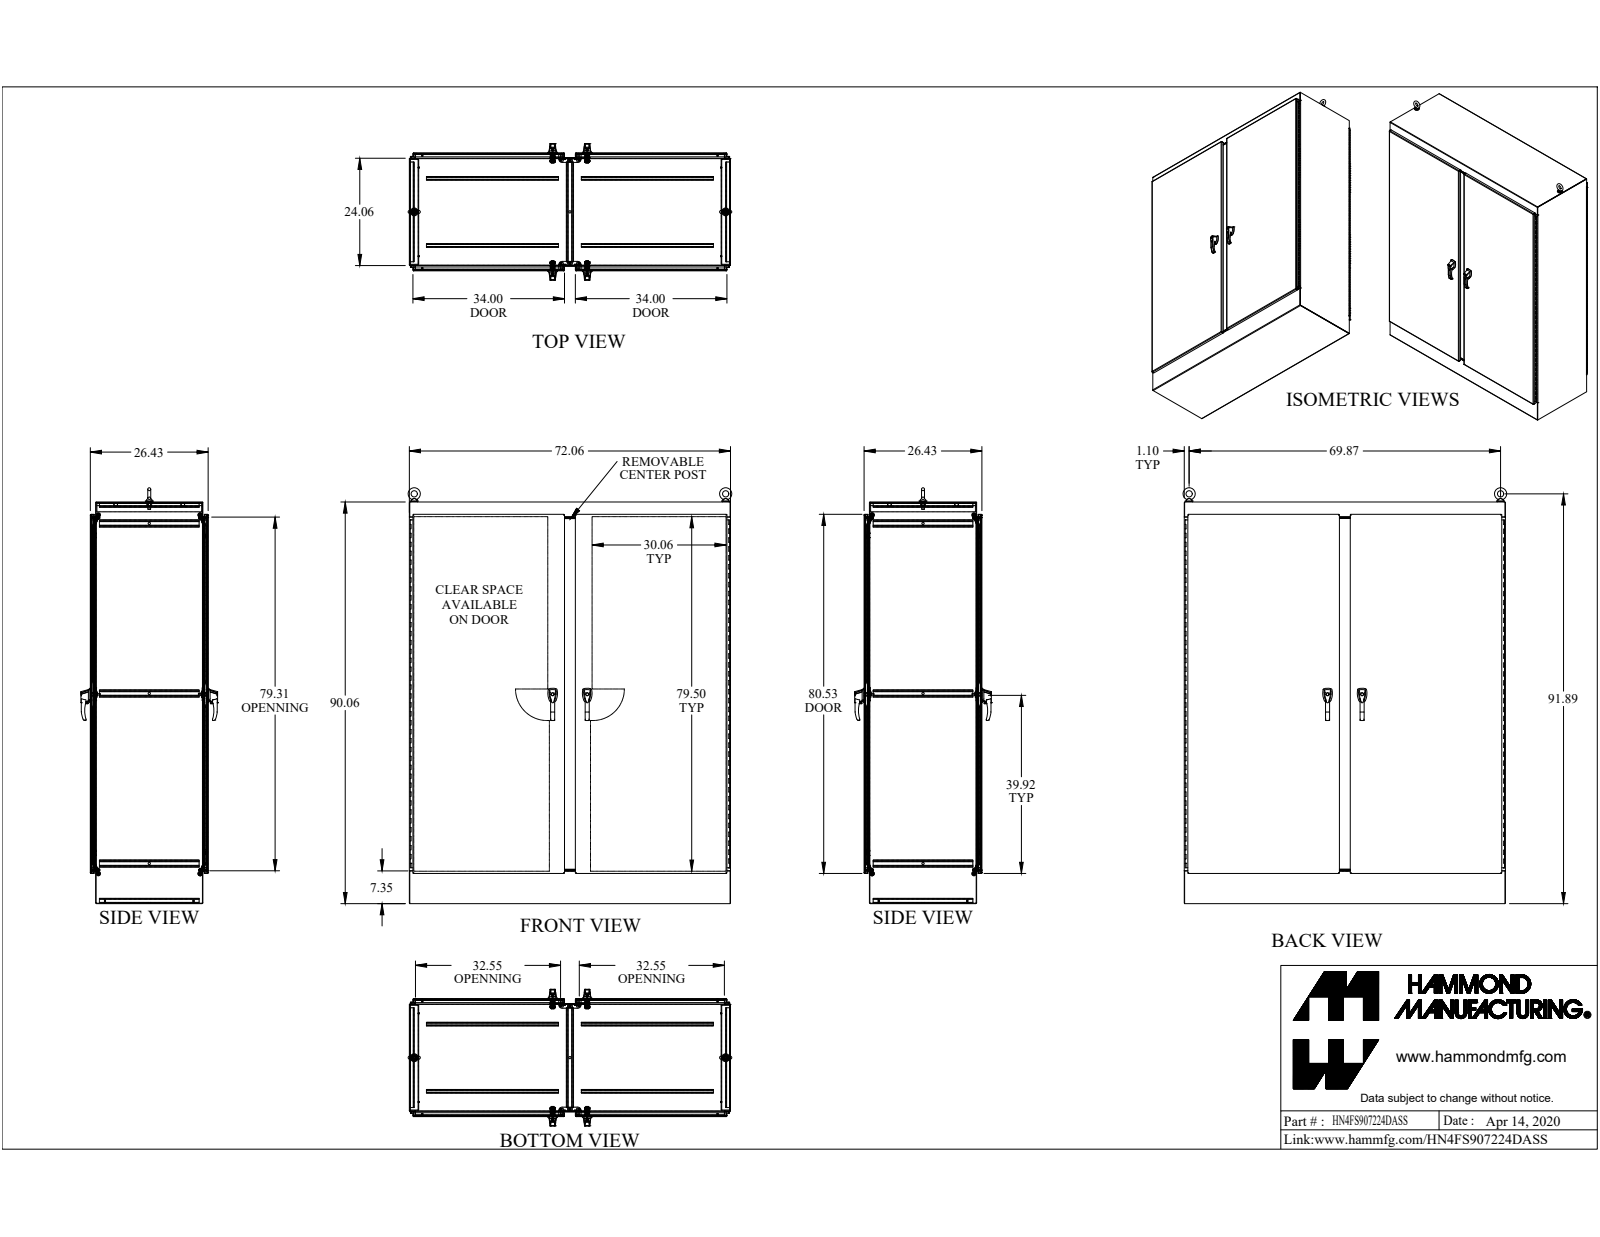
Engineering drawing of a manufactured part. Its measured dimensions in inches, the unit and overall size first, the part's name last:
Units: inches
Overall size (bounding box): 93.256 × 72.604 × 30.664
Round holes (diameter × count): ⌀0.304 ×26, ⌀0.25 ×12, ⌀0.35 ×9, ⌀0.313 ×8, ⌀0.281 ×7, ⌀0.39 ×7, ⌀0.201 ×6, ⌀0.257 ×6, ⌀0.28 ×6, ⌀0.313 ×6, ⌀0.413 ×6, ⌀0.11 ×4
Round bosses / shafts (diameter × count): ⌀0.75 ×8, ⌀0.44 ×8, ⌀1 ×6, ⌀0.63 ×6, ⌀0.313 ×6, ⌀0.293 ×6, ⌀0.25 ×6, ⌀0.246 ×6
Partial cylindrical surfaces — rounded edges, fillets, slot ends (radius × count): R0.043 ×60, R0.138 ×48, R0.1 ×46, R0.5 ×46, R0.125 ×43, R0.06 ×39, R0.017 ×32, R0.018 ×32
Main face-to-face distances: 0.095, 26.339, 26.244, 26.434, 71.965, 1.187, 25.152, 89.965, 71.87, 72.06
Hole centre spacings: 6, 70.584, 12, 71.345, 18, 72.595, 24, 74.311
Volume: 2 573 in³ · Surface area: 54 504 in²
Bodies: 189 solids, 5855 faces (3025 planar, 2354 cylindrical, 476 other)
Part name (STEP PRODUCT): HN4FS907224DASS
STEP written by: SolidWorks 2019 (CONFIG_CONTROL_DESIGN)
